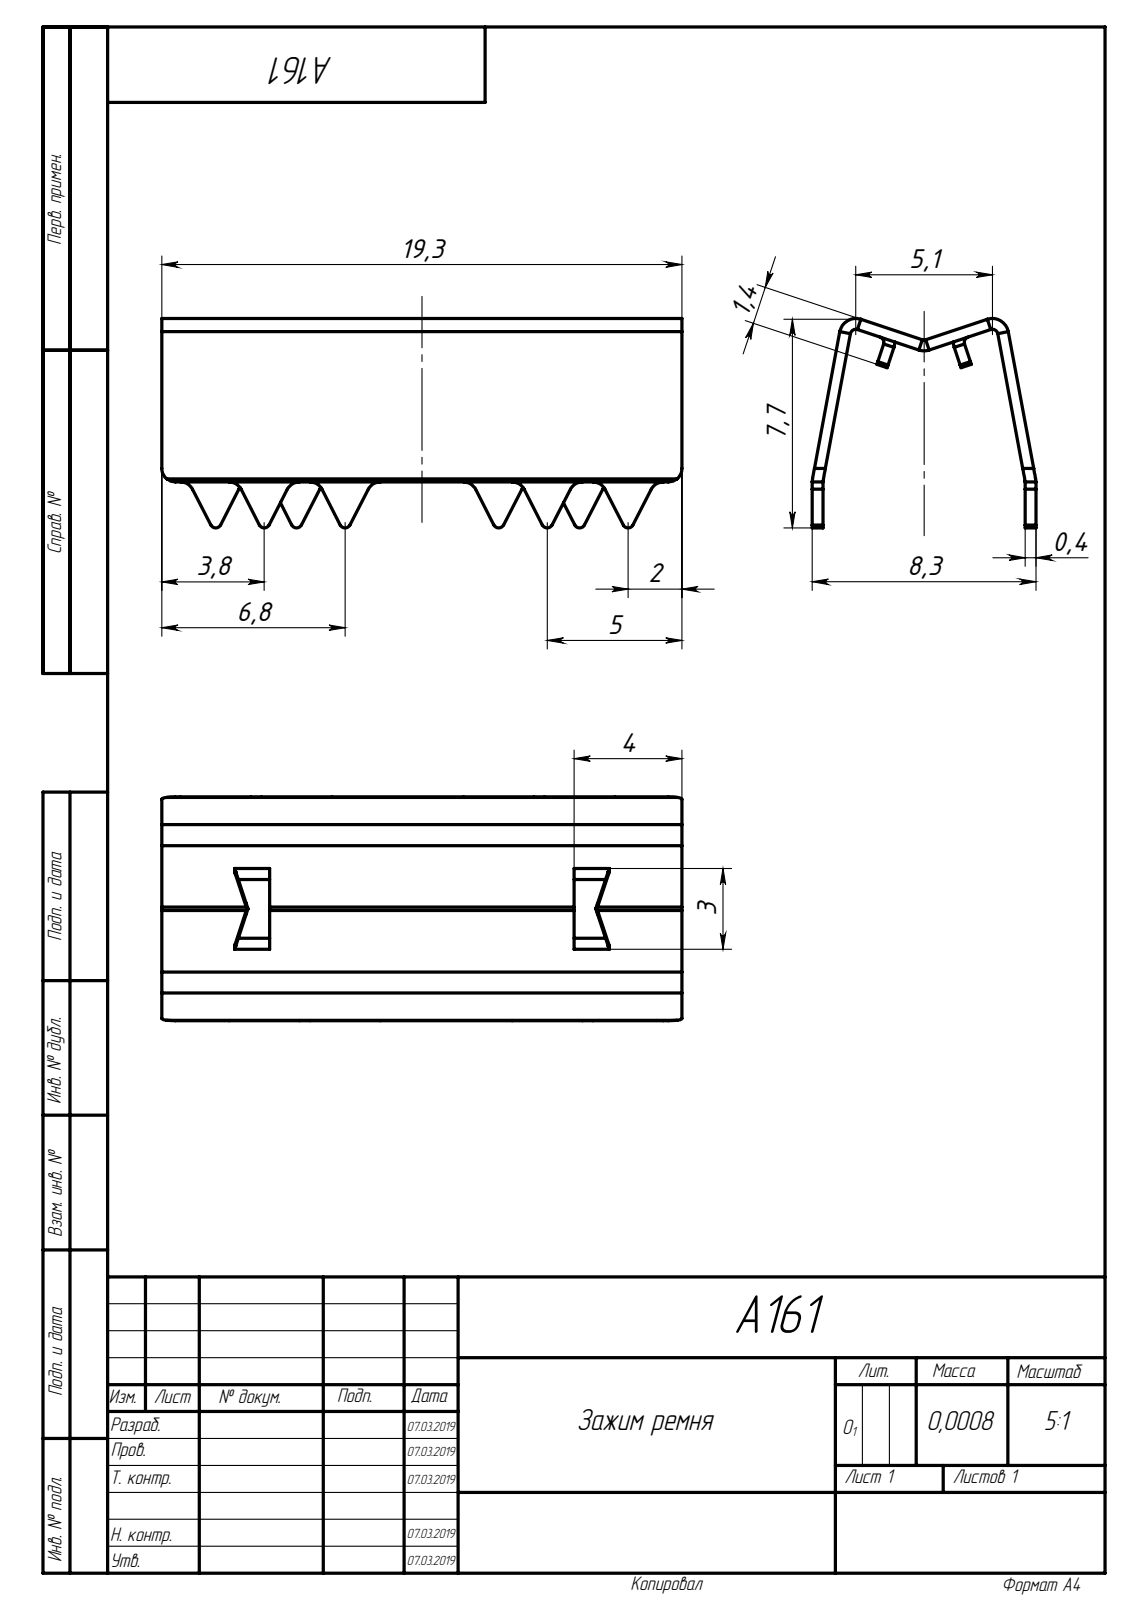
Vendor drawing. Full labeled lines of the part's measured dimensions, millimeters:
Part name (STEP PRODUCT): А161 Зажим ремня(подробная модель)
STEP written by: SolidWorks 2014 (AUTOMOTIVE_DESIGN)
Units: millimetres
Bodies: 1 solid, 172 faces (106 planar, 58 cylindrical, 8 other)
Overall size (bounding box): 19.3 × 8.3 × 7.78
Volume: 143 mm³ · Surface area: 759 mm²
Partial cylindrical surfaces — rounded edges, fillets, slot ends (radius × count): R0.2 ×23, R0.5 ×18, R0.6 ×7
Main face-to-face distances: 0.4, 7.9, 8.3, 7.5, 19.3, 9.33, 2.67, 1.6, 4, 15.3
